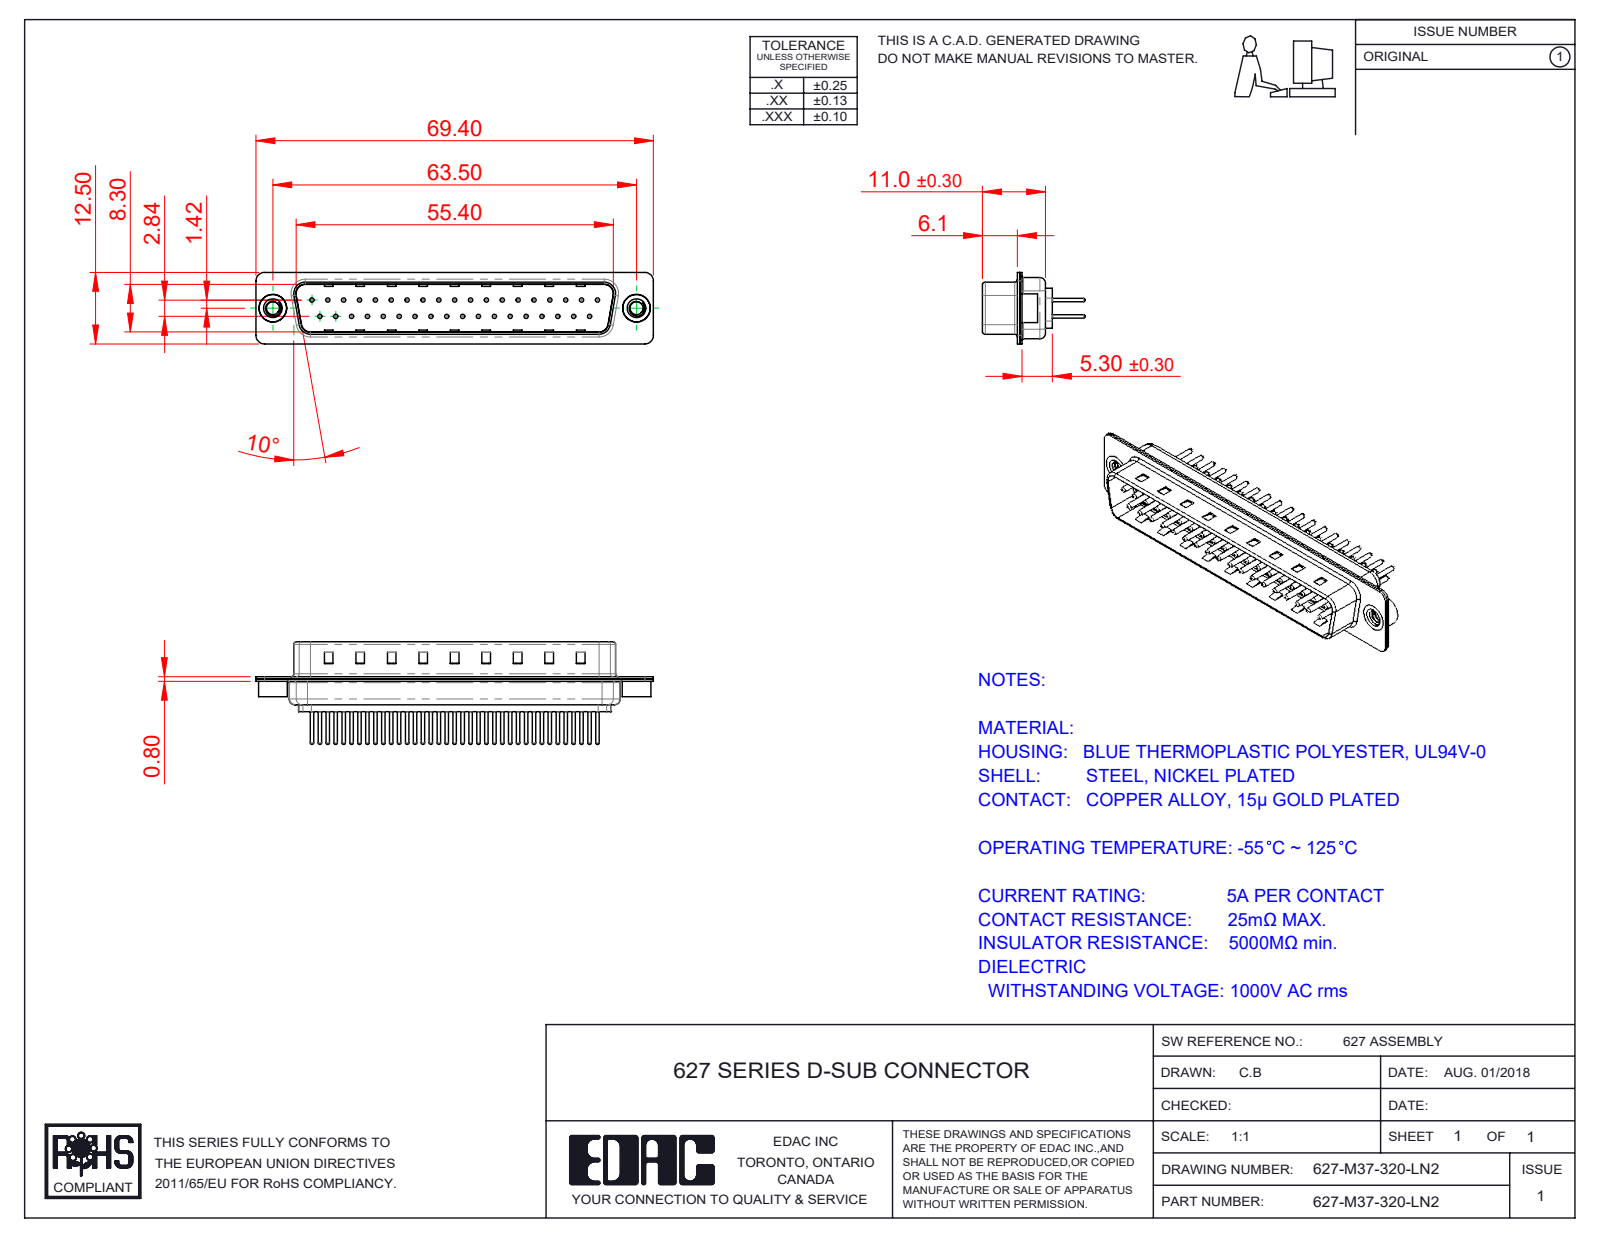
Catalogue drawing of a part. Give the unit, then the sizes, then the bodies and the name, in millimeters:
Units: millimetres
Overall size (bounding box): 69.4 × 17.9 × 12.5
Round holes (diameter × count): ⌀0.75 ×37, ⌀1.6 ×37, ⌀2 ×37, ⌀2.26 ×2, ⌀4 ×2, ⌀4.8 ×2
Round bosses / shafts (diameter × count): ⌀1.5 ×37, ⌀0.6 ×37, ⌀5 ×2, ⌀4.9 ×2
Partial cylindrical surfaces — rounded edges, fillets, slot ends (radius × count): R1.5 ×16, R2 ×12, R0.5 ×8, R1.6 ×8, R0.25 ×4, R0.6 ×4, R0.65 ×4, R0.9 ×4
Main face-to-face distances: 0.4, 0.8, 9.5, 9.1, 8.7, 9.9, 1.2, 5.7, 0.75, 0.35
Hole centre spacings: 2.77, 5.54, 3.16, 8.31, 11.08, 13.85, 16.62, 19.39
Volume: 3 768 mm³ · Surface area: 9 269 mm²
Bodies: 42 solids, 1781 faces (462 planar, 659 cylindrical, 660 other)
Part name (STEP PRODUCT): 627M Housing_37 Contacts; 627M Contact Row 2_20; 627M Contact Row 1_20; 627M 4-40 Threaded Rivet (+3 more)
STEP written by: SolidWorks 2020 (CONFIG_CONTROL_DESIGN)
